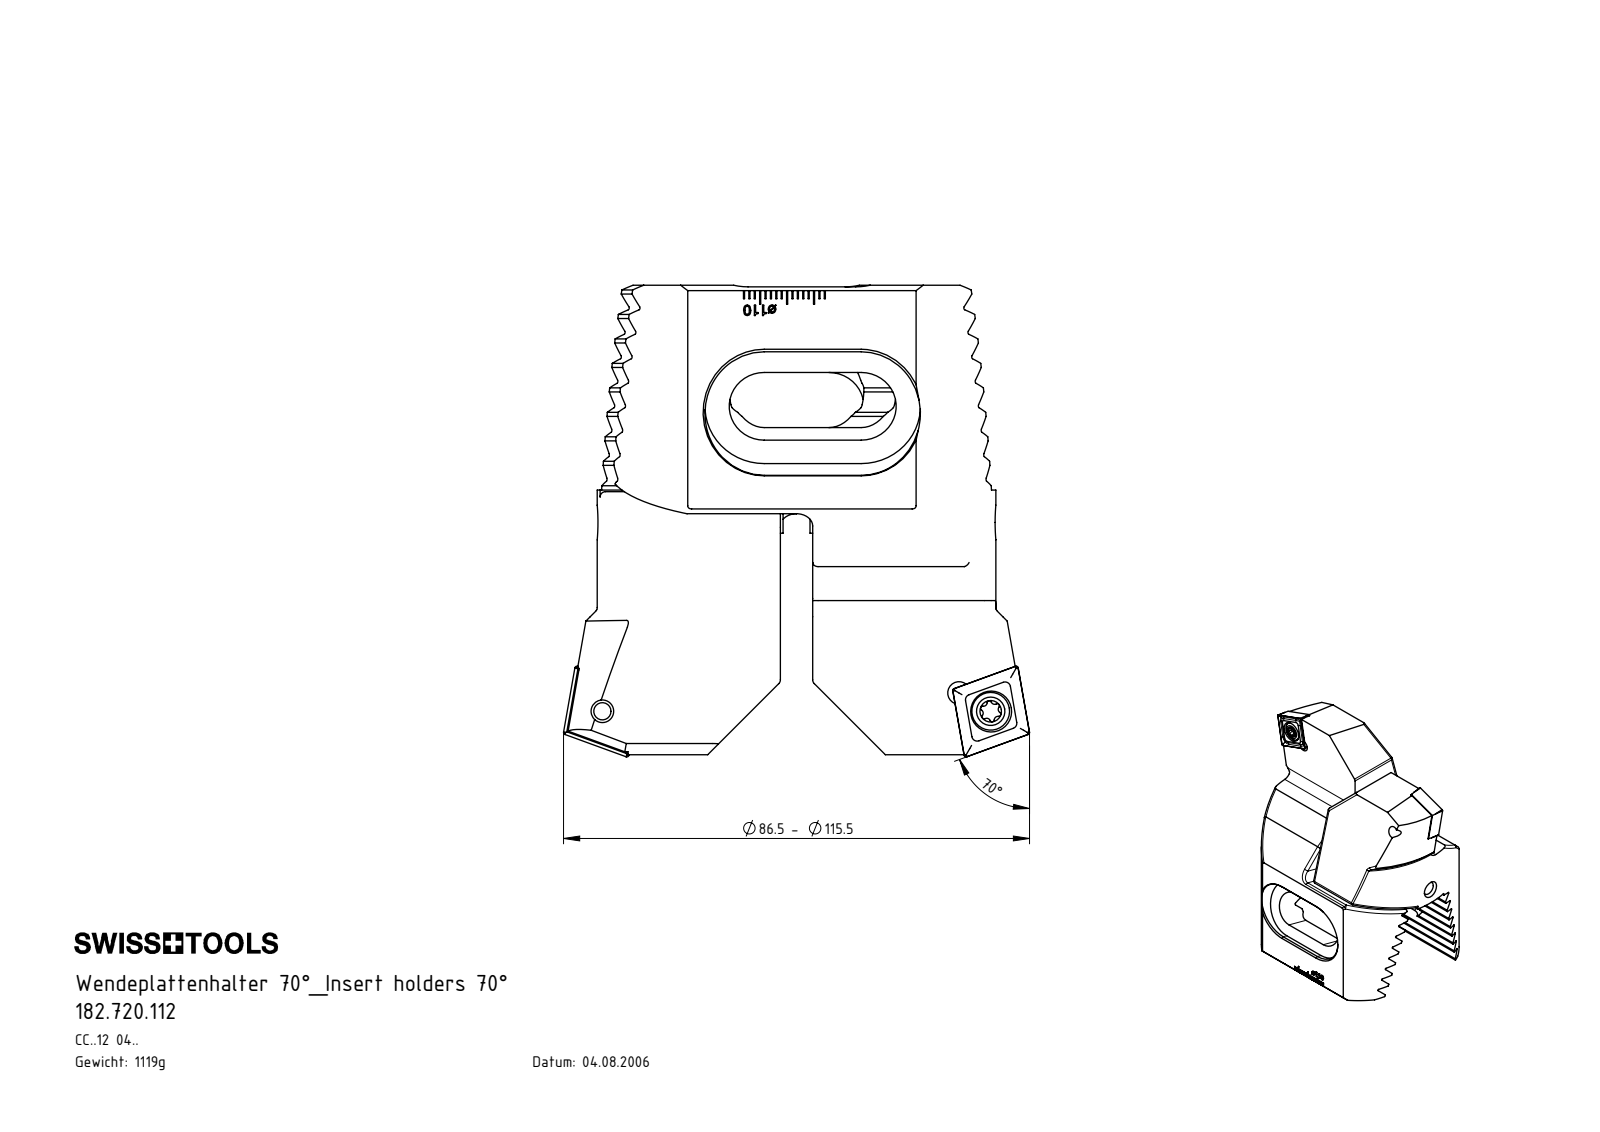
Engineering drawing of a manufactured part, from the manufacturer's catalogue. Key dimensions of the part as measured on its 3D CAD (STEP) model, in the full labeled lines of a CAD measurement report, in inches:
Part name (STEP PRODUCT): Z72-xxx.001.050_C_CC 12_70ø; CCMT120404; 182.720.112; WCC-ER2.001.010_A (+1 more)
STEP written by: SolidWorks 2017 (CONFIG_CONTROL_DESIGN)
Units: inches
Bodies: 8 solids, 730 faces (398 planar, 138 cylindrical, 194 other)
Overall size (bounding box): 3.445 × 3.406 × 2.291
Volume: 8.781 in³ · Surface area: 58.52 in²
Round holes (diameter × count): ⌀0.165 ×4, ⌀0.079 ×2, ⌀0.217 ×2, ⌀0.299 ×2, ⌀0.197 ×1
Round bosses / shafts (diameter × count): ⌀0.276 ×2, ⌀0.197 ×2, ⌀0.236 ×1, ⌀0.157 ×1
Partial cylindrical surfaces — rounded edges, fillets, slot ends (radius × count): R0.013 ×16, R0.039 ×16, R0.015 ×12, R0.027 ×8, R0.118 ×6, R0.027 ×4, R0.256 ×4, R0.433 ×4
Main face-to-face distances: 0.16, 0.32, 1.134, 1.157, 0.802, 0.481, 2.291, 0.641, 0.801, 0.962
Hole centre spacings: 0.267, 0.271, 0.787, 2.61, 2.613, 2.841, 1.521, 2.375
